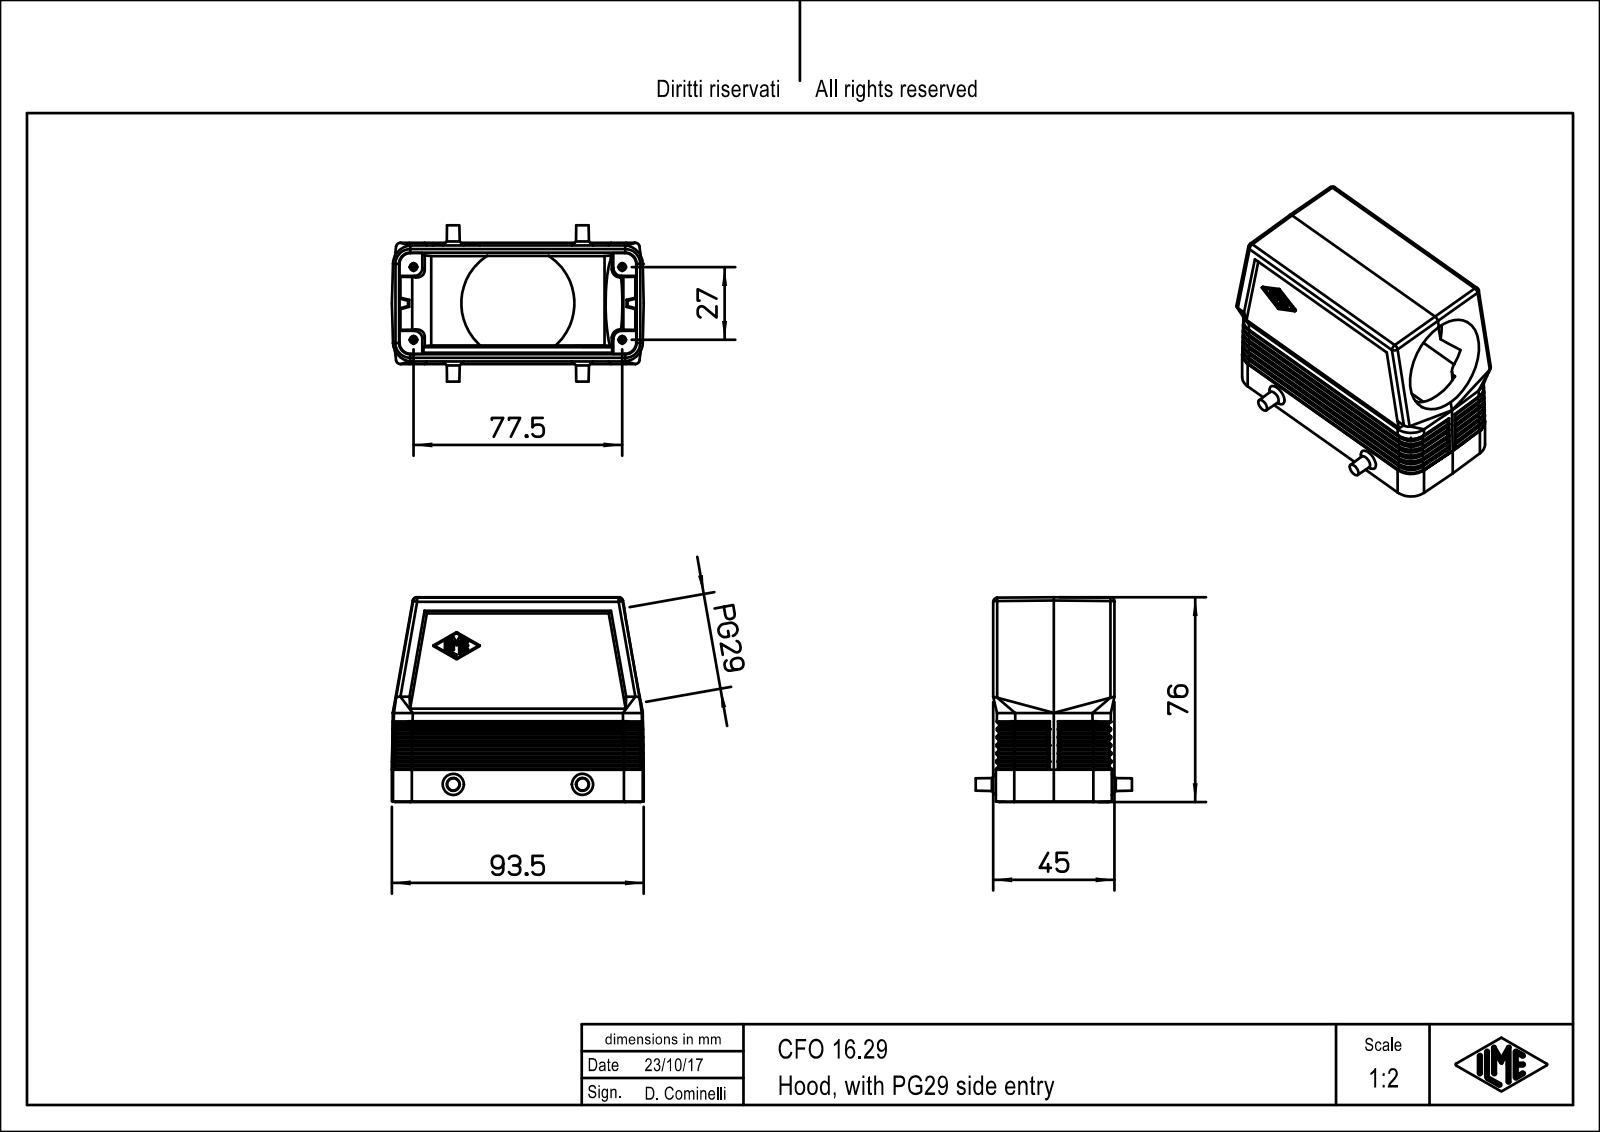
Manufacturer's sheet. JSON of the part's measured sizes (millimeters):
{"part_name": "CFO_16.29", "step_written_by": "PTC Creo Elements/Direct Modeling 19.0E 27-Jun-2016 (C) Parametric Technology GmbH (AUTOMOTIVE_DESIGN)", "units": "millimeters", "bodies": {"solids": 1, "faces": 527, "planar": 240, "cylindrical": 135, "other": 152}, "overall_size": [93.5, 76, 58], "volume_mm3": 86376, "surface_area_mm2": 43516, "round_holes": [[35.7, 1]], "partial_cylinders_radius": [[0.5, 78], [0.33, 15], [1.5, 10], [7, 8], [3, 4], [4.2, 4], [0.17, 3], [0.67, 1]], "face_to_face_distances": [43, 2.01, 2, 8.5, 4, 3.2, 1, 44, 6, 6.01]}
